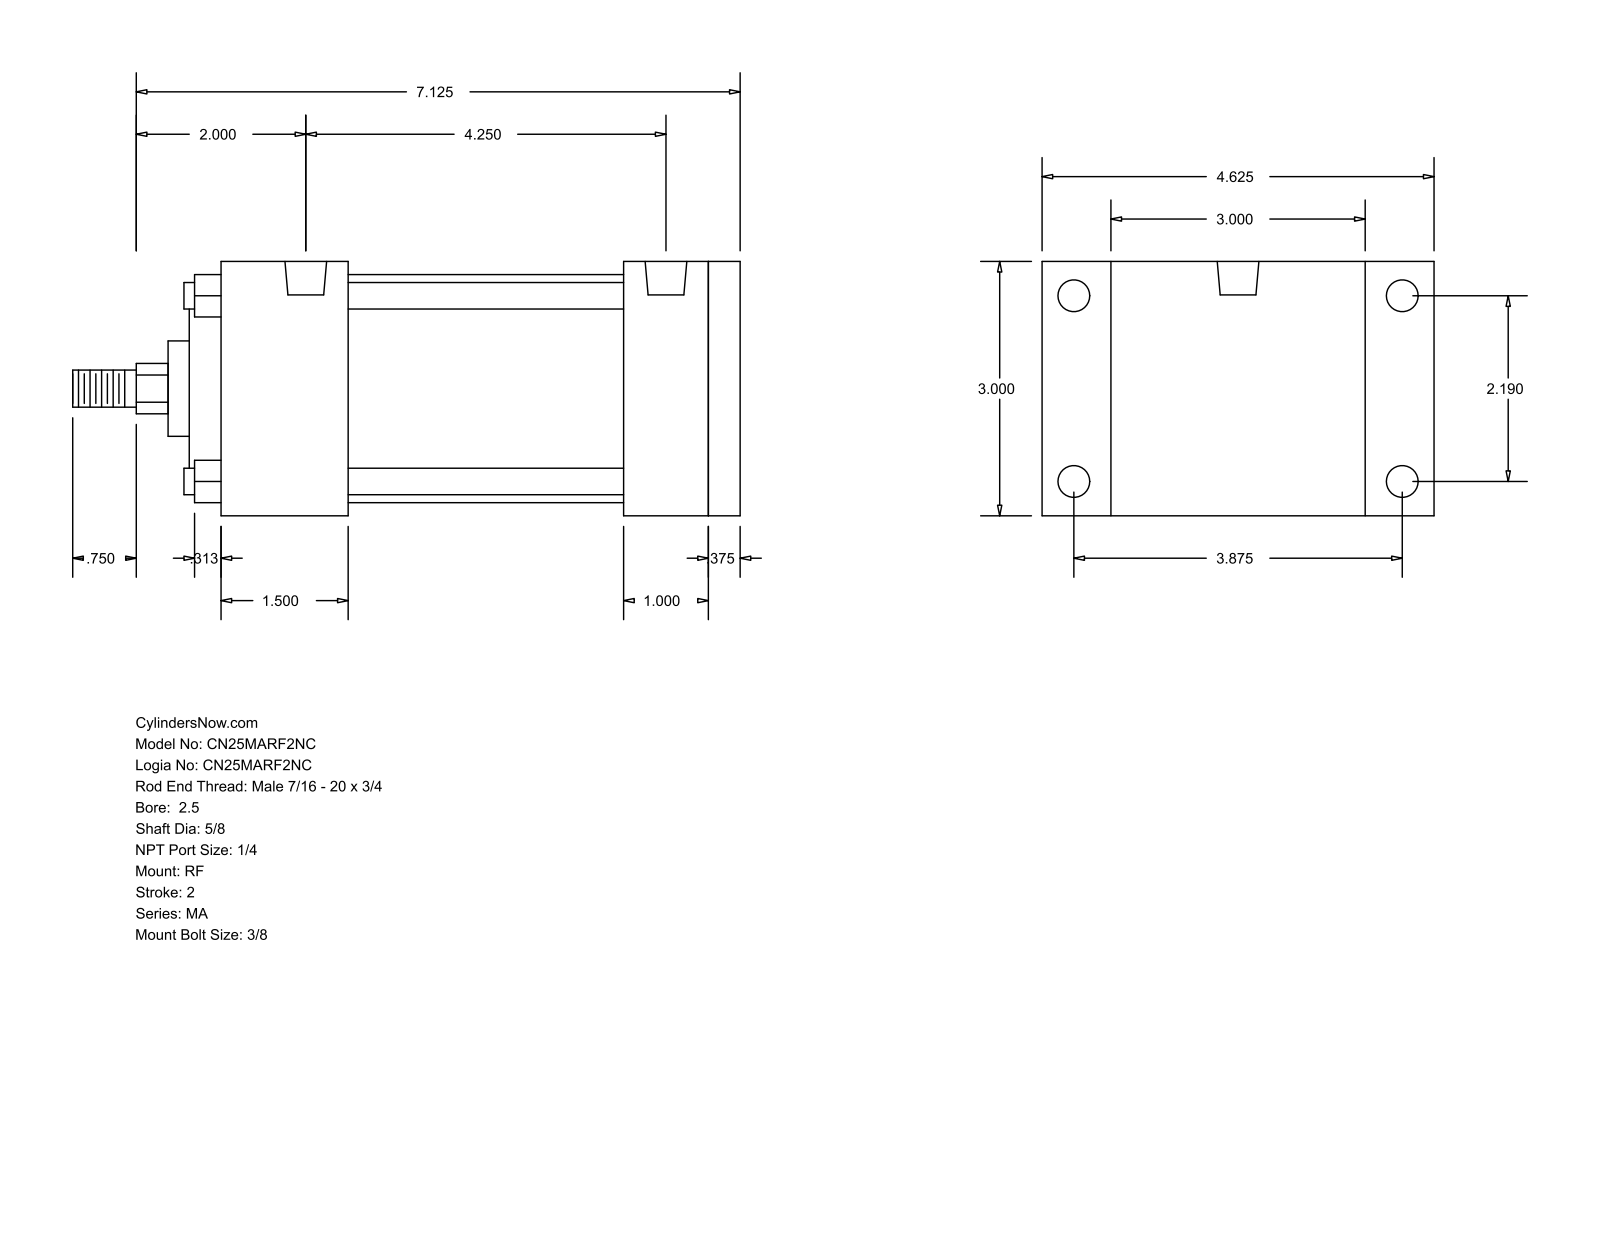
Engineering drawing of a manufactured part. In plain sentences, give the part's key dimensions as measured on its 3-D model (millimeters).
The part is named "MA_RF__0250_0.625". Its 3-D file was written by "GSSL Pune (CONFIG_CONTROL_DESIGN)". It is 0 solids with 94 faces: 65 planar, 29 cylindrical and 0 other. Overall it measures 200.03 by 117.47 by 76.2 millimeters. Round holes: 4 of diameter 7.94, 4 of diameter 9.53, 2 of diameter 12.49. Round bosses or shafts: 4 of diameter 7.94, 1 of diameter 68.33, 1 of diameter 50.8, 1 of diameter 28.57, 1 of diameter 15.88, 1 of diameter 11.11. Partial cylindrical surfaces (rounded edges, fillets, slot ends): 1 of radius 7.54. The main face-to-face distances are 76.2, 155.57, 9.52, 146.05, 25.4, 82.55, 38.1, 120.65, 107.95, 117.47. The hole center spacings are 55.62, 98.42, 107.95, 113.05.
